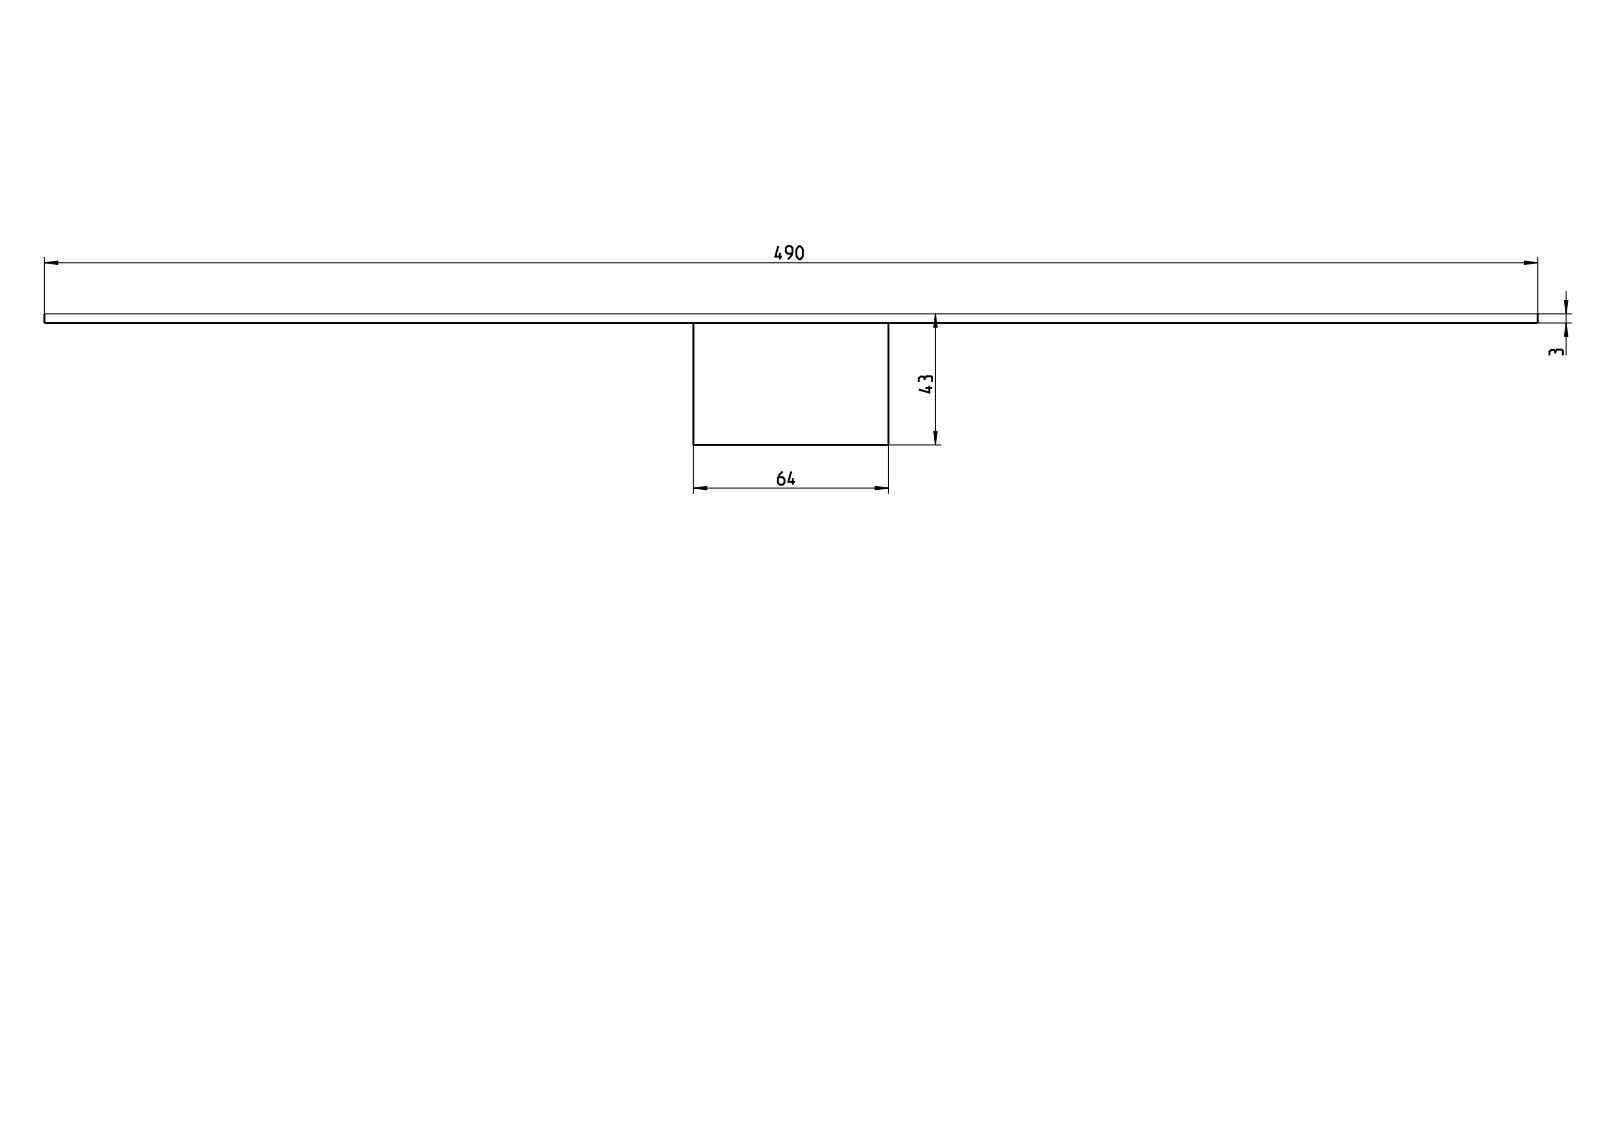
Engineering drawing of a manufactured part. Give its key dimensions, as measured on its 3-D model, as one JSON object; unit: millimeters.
{"part_name": "T-01192; AUSLASS; BKG5002LA_ASM", "step_written_by": "CREO PARAMETRIC BY PTC INC, 2022024 (AUTOMOTIVE_DESIGN)", "units": "millimeters", "bodies": {"solids": 2, "faces": 16, "planar": 16, "cylindrical": 0, "other": 0}, "overall_size": [499, 490, 43], "volume_mm3": 828136, "surface_area_mm2": 503788, "face_to_face_distances": [3, 37, 40, 43, 64, 212.95, 276.95, 490, 277.05, 213.05]}
